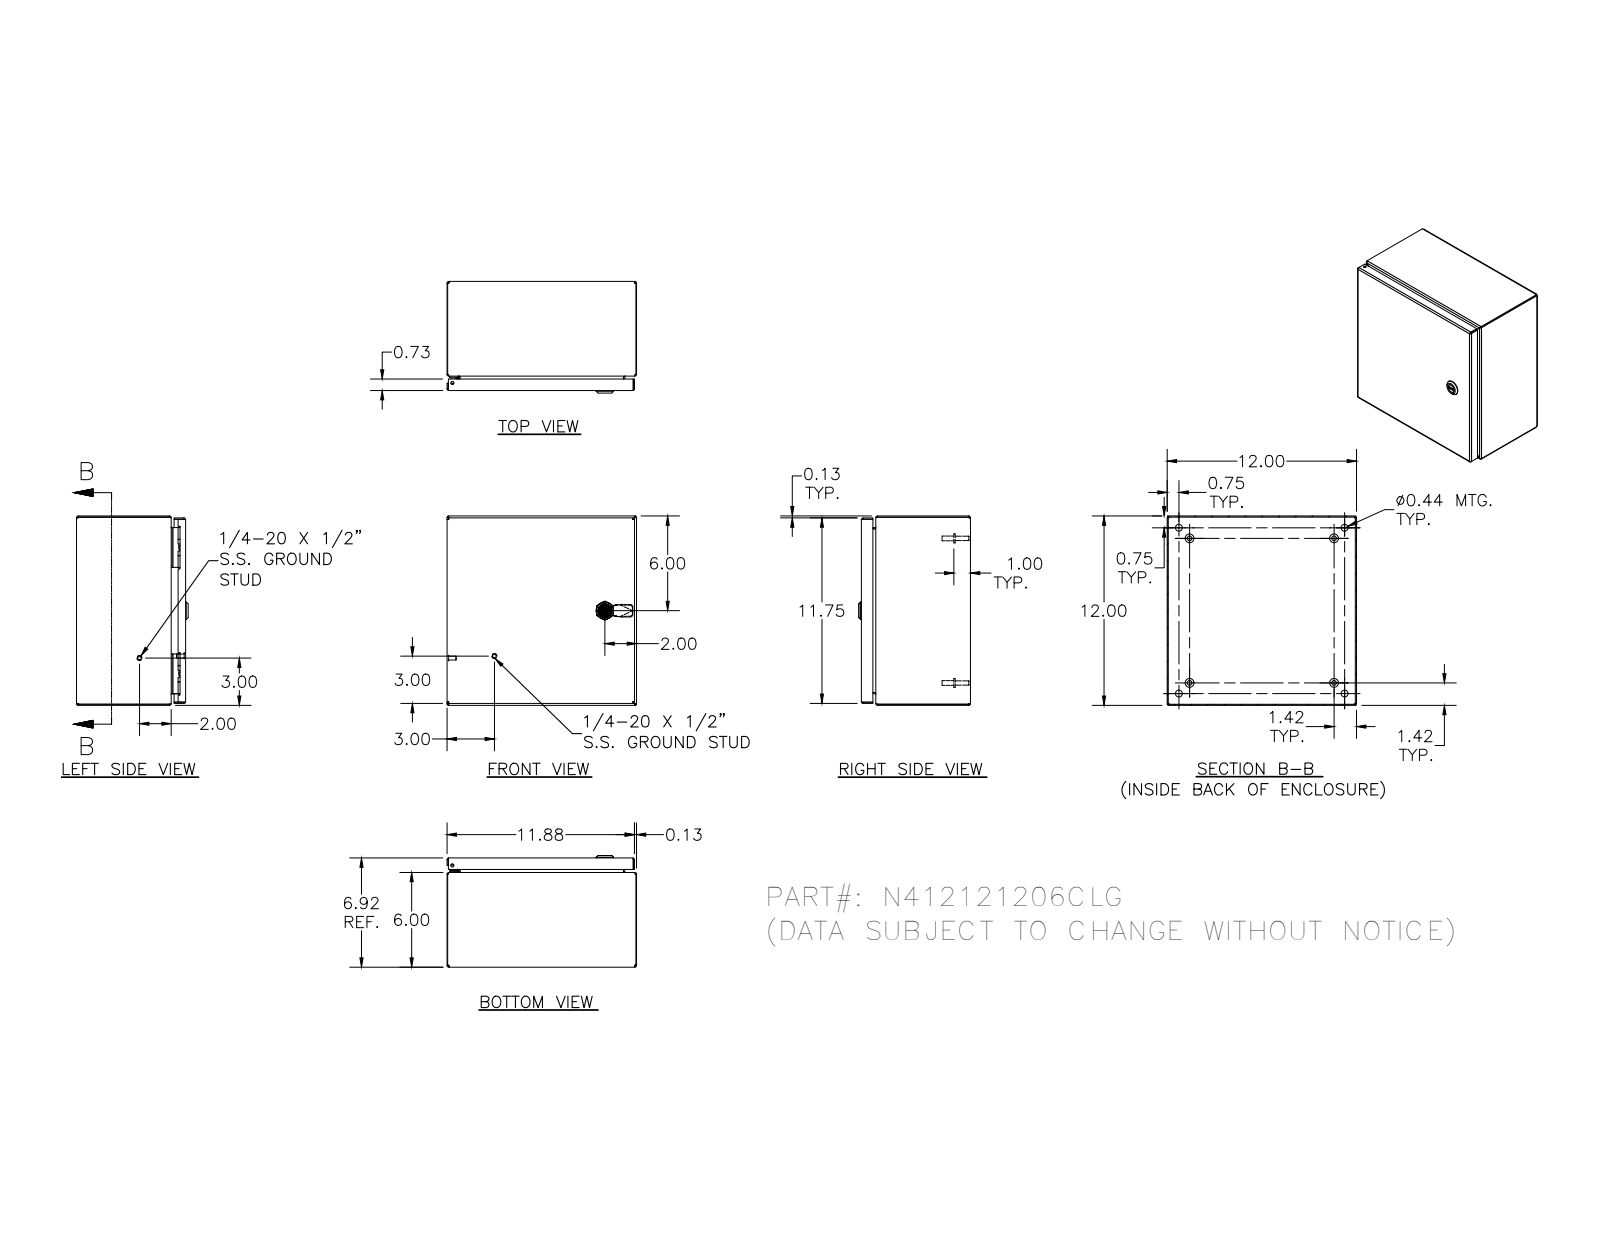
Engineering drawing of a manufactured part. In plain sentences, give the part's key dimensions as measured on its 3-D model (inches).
The part is named "N412121206CLG". Its 3-D file was written by "SolidWorks 2018 (AUTOMOTIVE_DESIGN)". It is 33 solids with 1449 faces: 530 planar, 547 cylindrical and 372 other. Overall it measures 12 by 12 by 7.075 inches. Its volume is 50.57 cubic inches and its surface area 1 380 square inches. Round holes: 5 of diameter 0.188, 4 of diameter 0.093, 4 of diameter 0.152, 4 of diameter 0.167, 4 of diameter 0.172, 4 of diameter 0.437, 2 of diameter 0.156, 1 of diameter 0.187, 1 of diameter 0.197, 1 of diameter 0.315, 1 of diameter 0.394, 1 of diameter 0.402. Round bosses or shafts: 10 of diameter 0.25, 4 of diameter 0.563, 4 of diameter 0.36, 4 of diameter 0.32, 4 of diameter 0.3, 4 of diameter 0.275, 4 of diameter 0.256, 4 of diameter 0.164. Partial cylindrical surfaces (rounded edges, fillets, slot ends): 30 of radius 0.012, 30 of radius 0.031, 26 of radius 0.05, 20 of radius 0.105, 18 of radius 0.016, 16 of radius 0.125, 13 of radius 0.02, 8 of radius 0.032. The main face-to-face distances are 0.074, 6.843, 0.074, 11.926, 11.852, 11.926, 12, 6.769, 6.917, 0.917. The hole center spacings are 8, 0.66, 10.5, 0.656, 1.307, 1.965, 0.5, 0.984.
